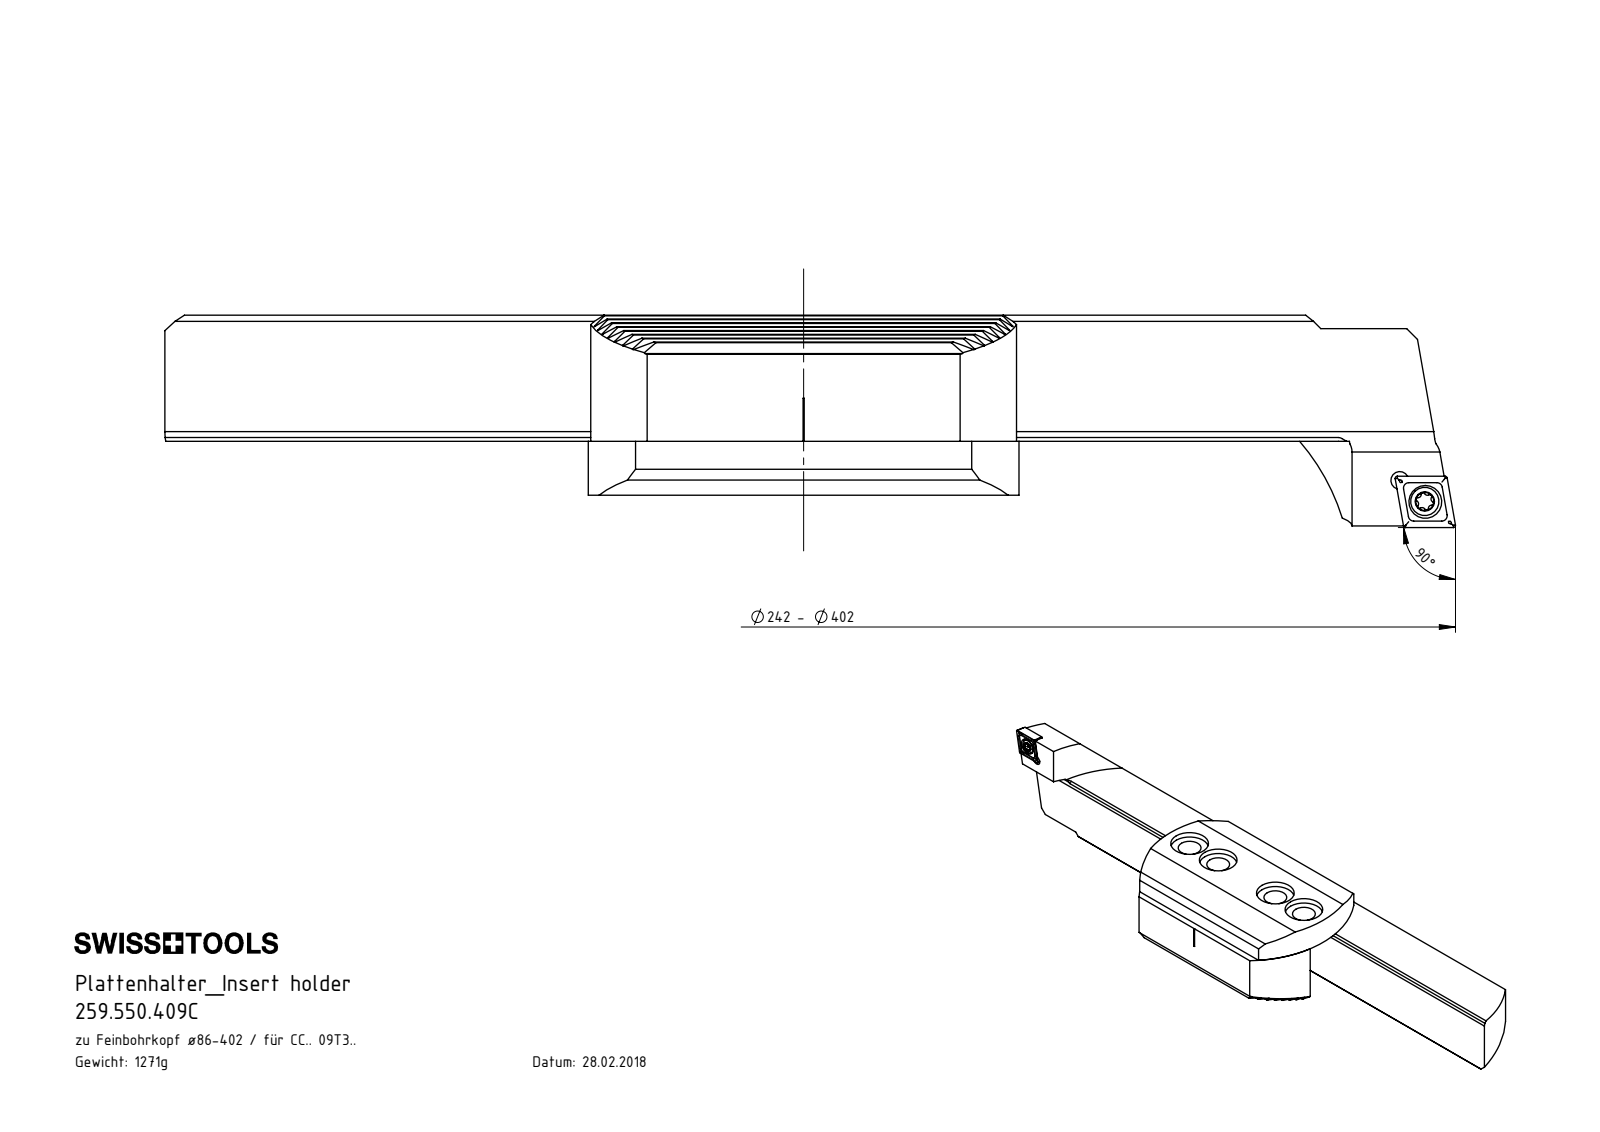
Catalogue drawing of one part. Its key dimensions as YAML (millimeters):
part_name: "WCB-ER2.001.009_A; F00-WCB.242.001_C; 259.550.409C; F00-WCB.136.002_A (+3 more)"
step_written_by: "SolidWorks 2017 (CONFIG_CONTROL_DESIGN)"
units: millimeters
bodies: {solids: 5, faces: 992, planar: 604, cylindrical: 67, other: 321}
overall_size: [239.57, 55, 39.4]
volume: 161949
surface_area: 41929
round_holes:
  - {diameter: 8.5, count: 4}
  - {diameter: 14, count: 4}
  - {diameter: 3.3, count: 2}
  - {diameter: 4.4, count: 1}
  - {diameter: 6.1, count: 1}
round_bosses_or_shafts:
  - {diameter: 5.25, count: 1}
  - {diameter: 4, count: 1}
partial_cylinders:
  - {radius: 0.2, count: 16}
  - {radius: 0.34, count: 6}
  - {radius: 0.59, count: 6}
  - {radius: 40, count: 6}
  - {radius: 0.8, count: 1}
face_to_face_distances: [2.38, 4.76, 21.3, 7.14, 33.7, 9.52, 4.77, 7.15, 9.53, 11.91]
hole_center_spacings: [15, 45, 6.06, 6.19, 30, 60]
